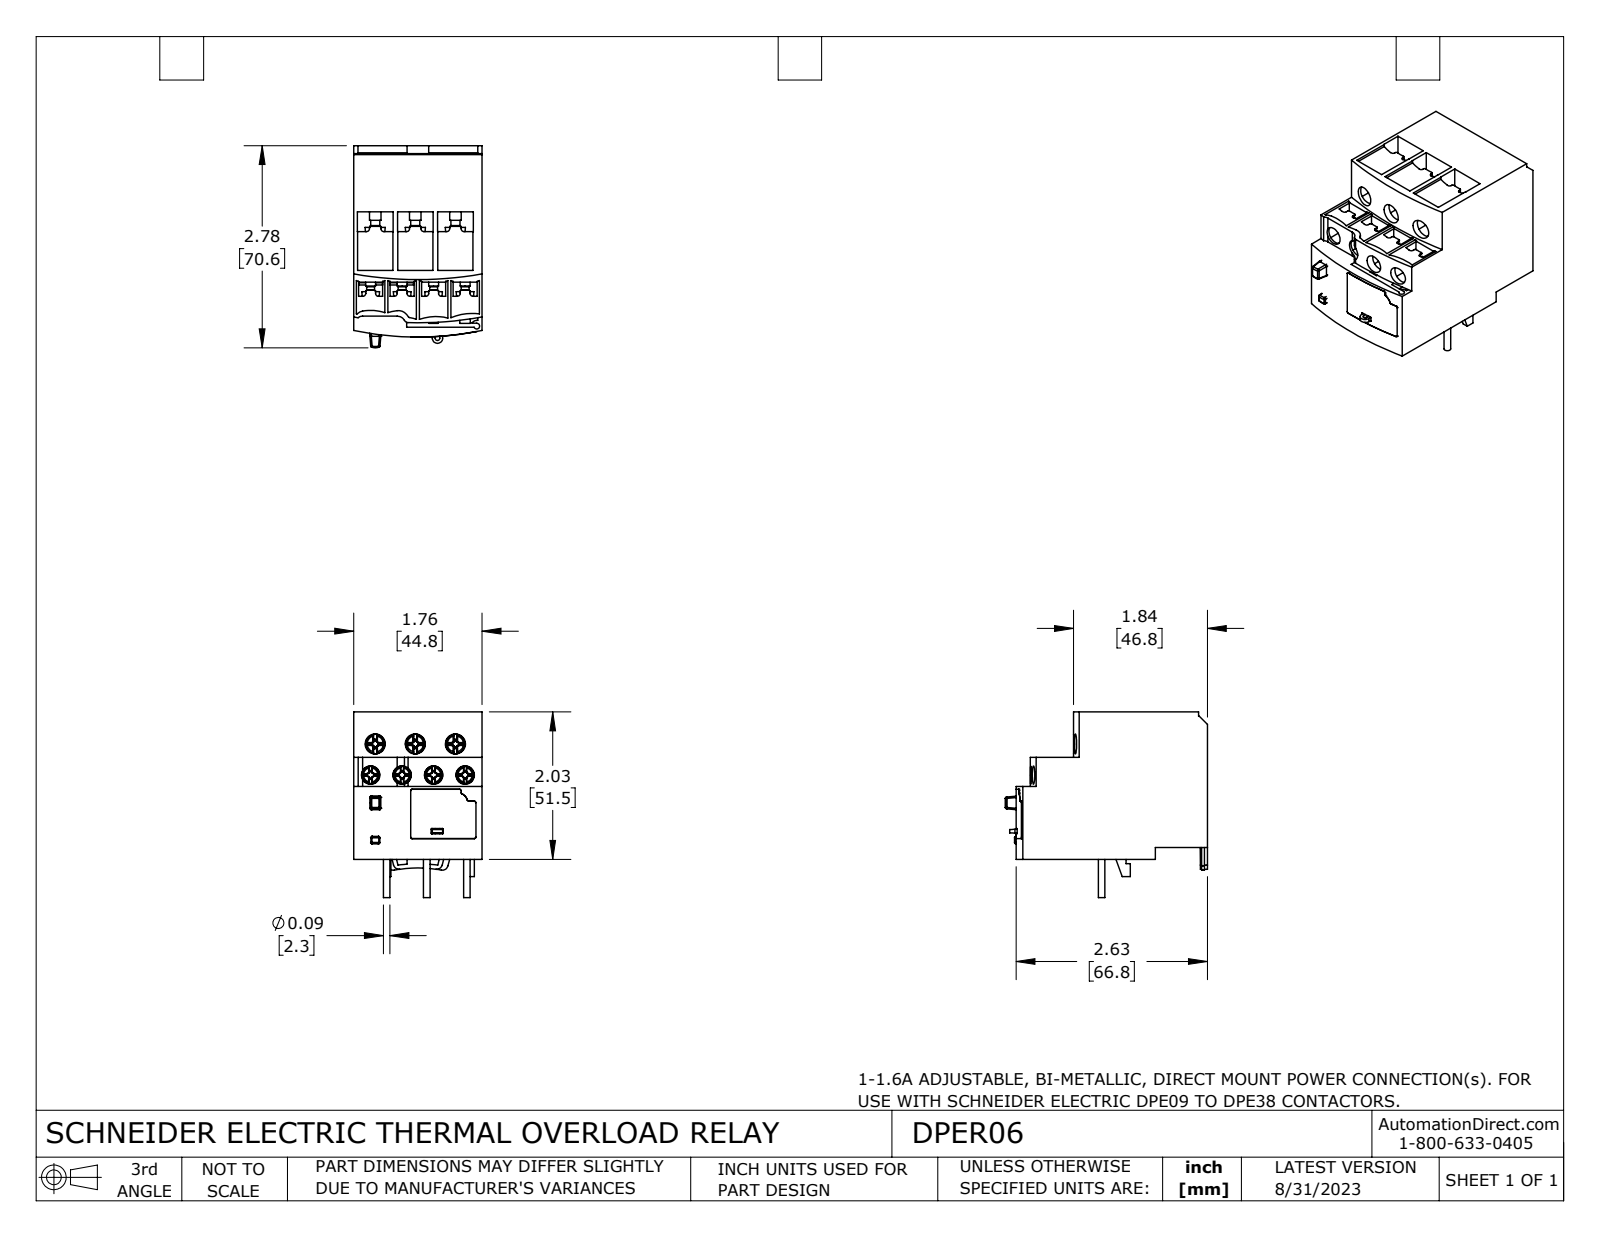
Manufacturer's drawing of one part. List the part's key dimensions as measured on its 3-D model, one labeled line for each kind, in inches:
Part name (STEP PRODUCT): DPER06
STEP written by: SolidWorks 2021 (CONFIG_CONTROL_DESIGN)
Units: inches
Bodies: 16 solids, 1212 faces (676 planar, 269 cylindrical, 267 other)
Overall size (bounding box): 2.778 × 2.553 × 1.764
Volume: 6.953 in³ · Surface area: 47.15 in²
Round holes (diameter × count): ⌀0.252 ×4, ⌀0.276 ×3, ⌀0.079 ×2, ⌀0.118 ×2, ⌀0.059 ×1, ⌀0.244 ×1
Round bosses / shafts (diameter × count): ⌀0.091 ×12, ⌀0.138 ×4, ⌀0.108 ×4, ⌀0.157 ×3, ⌀0.154 ×3, ⌀0.124 ×3, ⌀0.118 ×1, ⌀0.107 ×1
Partial cylindrical surfaces — rounded edges, fillets, slot ends (radius × count): R0.02 ×52, R0.039 ×22, R0.004 ×19, R0.012 ×8, R0.008 ×6, R0.63 ×6, R0.079 ×4, R0.024 ×2
Main face-to-face distances: 1.764, 0.165, 2.028, 1.863, 0.909, 0.551, 0.618, 1.409, 1.245, 2.497
Hole centre spacings: 0.433, 0.551, 0.866, 0.334, 0.381, 0.404, 0.422, 0.449
